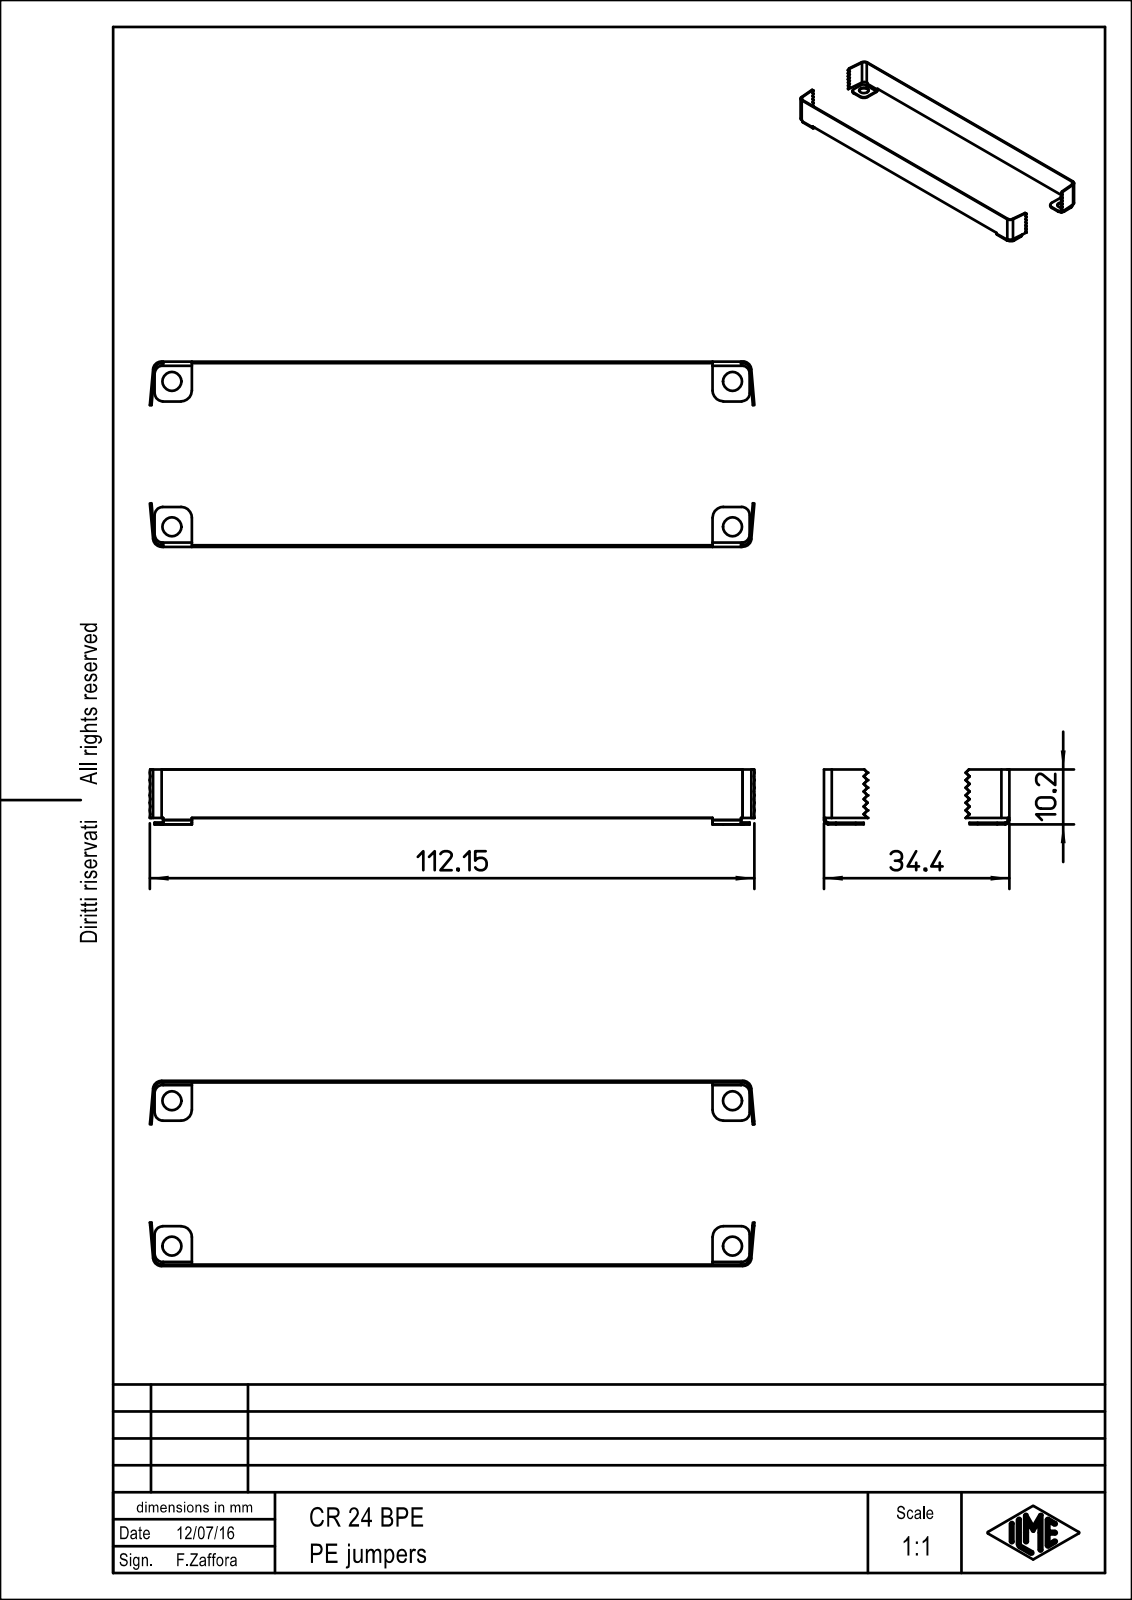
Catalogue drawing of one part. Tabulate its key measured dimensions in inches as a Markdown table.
| quantity | value |
| --- | --- |
| part name | 54198_A; 54198_A.1; CR_24_BPE |
| STEP written by | Creo Elements/Direct Modeling 18.1F 24-Jul-2014 (C) Parametric Technology GmbH (AUTOMOTIVE_DESIGN) |
| units | inches |
| bodies | 2 solids, 136 faces (100 planar, 36 cylindrical, 0 other) |
| overall size | 4.415 × 1.354 × 0.402 |
| volume | 0.044 in³ |
| surface area | 7.783 in² |
| round holes (diameter × count) | 0.138 × 4 |
| partial cylindrical surfaces (radius × count) | 0.059 × 8, 0.051 × 4, 0.063 × 4, 0.079 × 4, 0.02 × 2, 0.031 × 2 |
| main face-to-face distances | 1.343, 1.354, 1.331, 4.448, 4.437, 4.46, 0.402, 0.39, 0.047, 0.035 |
| hole center spacings | 1.063, 4.094, 4.23 |
